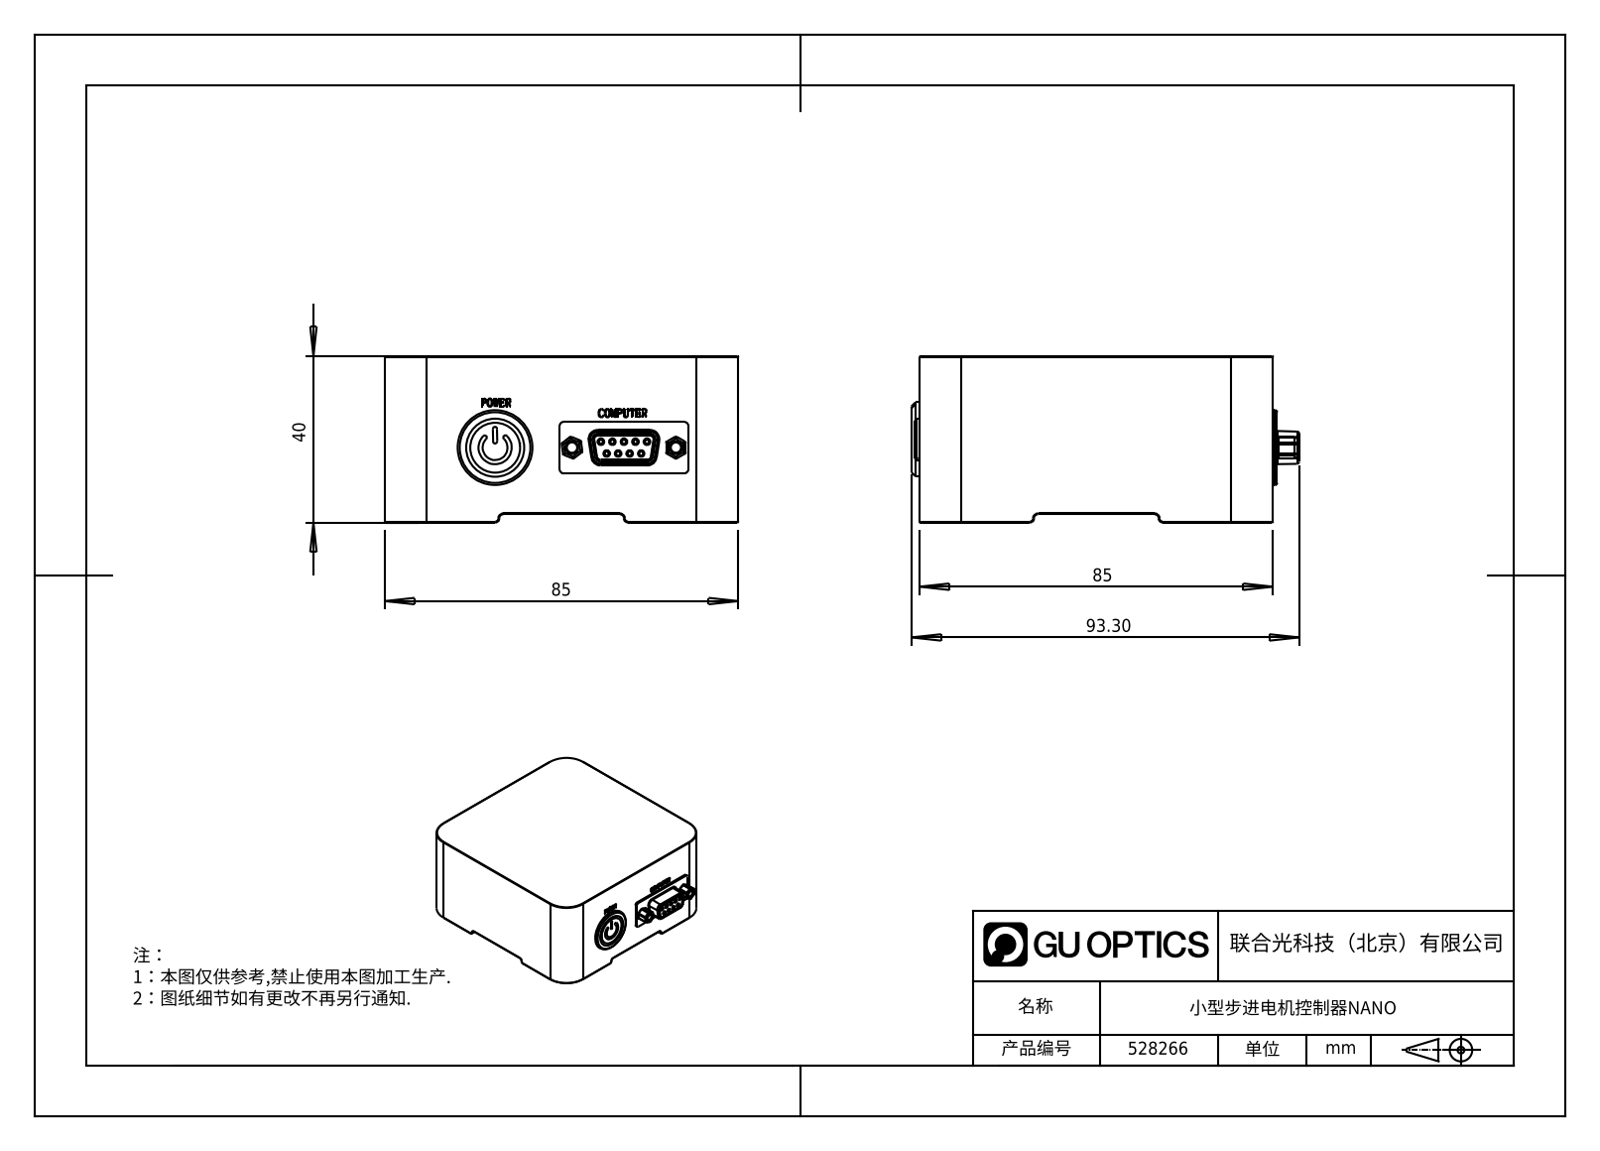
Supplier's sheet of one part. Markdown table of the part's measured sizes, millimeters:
| quantity | value |
| --- | --- |
| part name | 528266 |
| STEP written by | SolidWorks 2020 (CONFIG_CONTROL_DESIGN) |
| units | millimeters |
| bodies | 11 solids, 1189 faces (588 planar, 284 cylindrical, 317 other) |
| overall size | 91.3 × 85 × 40 |
| volume | 131 700 mm³ |
| surface area | 65 736 mm² |
| round holes (diameter × count) | 2.05 × 12, 1 × 9, 1.1 × 9, 2.9 × 8, 2.5 × 2, 3.2 × 2, 9.1 × 1, 14 × 1, 15.1 × 1, 16.1 × 1 |
| round bosses / shafts (diameter × count) | 1.5 × 9, 4.4 × 4, 2.5 × 4, 3 × 2, 18 × 1, 16 × 1, 12 × 1 |
| partial cylindrical surfaces (radius × count) | 0.5 × 44, 0.3 × 24, 1 × 24, 0.2 × 16, 2 × 16, 1.45 × 6, 0.1 × 4, 0.92 × 4 |
| main face-to-face distances | 5, 2, 36, 38, 3, 80, 33, 35, 85, 75 |
| hole center spacings | 3.16, 9.58, 32.69, 40.58, 41.88, 51.22, 2.77, 5.54 |
